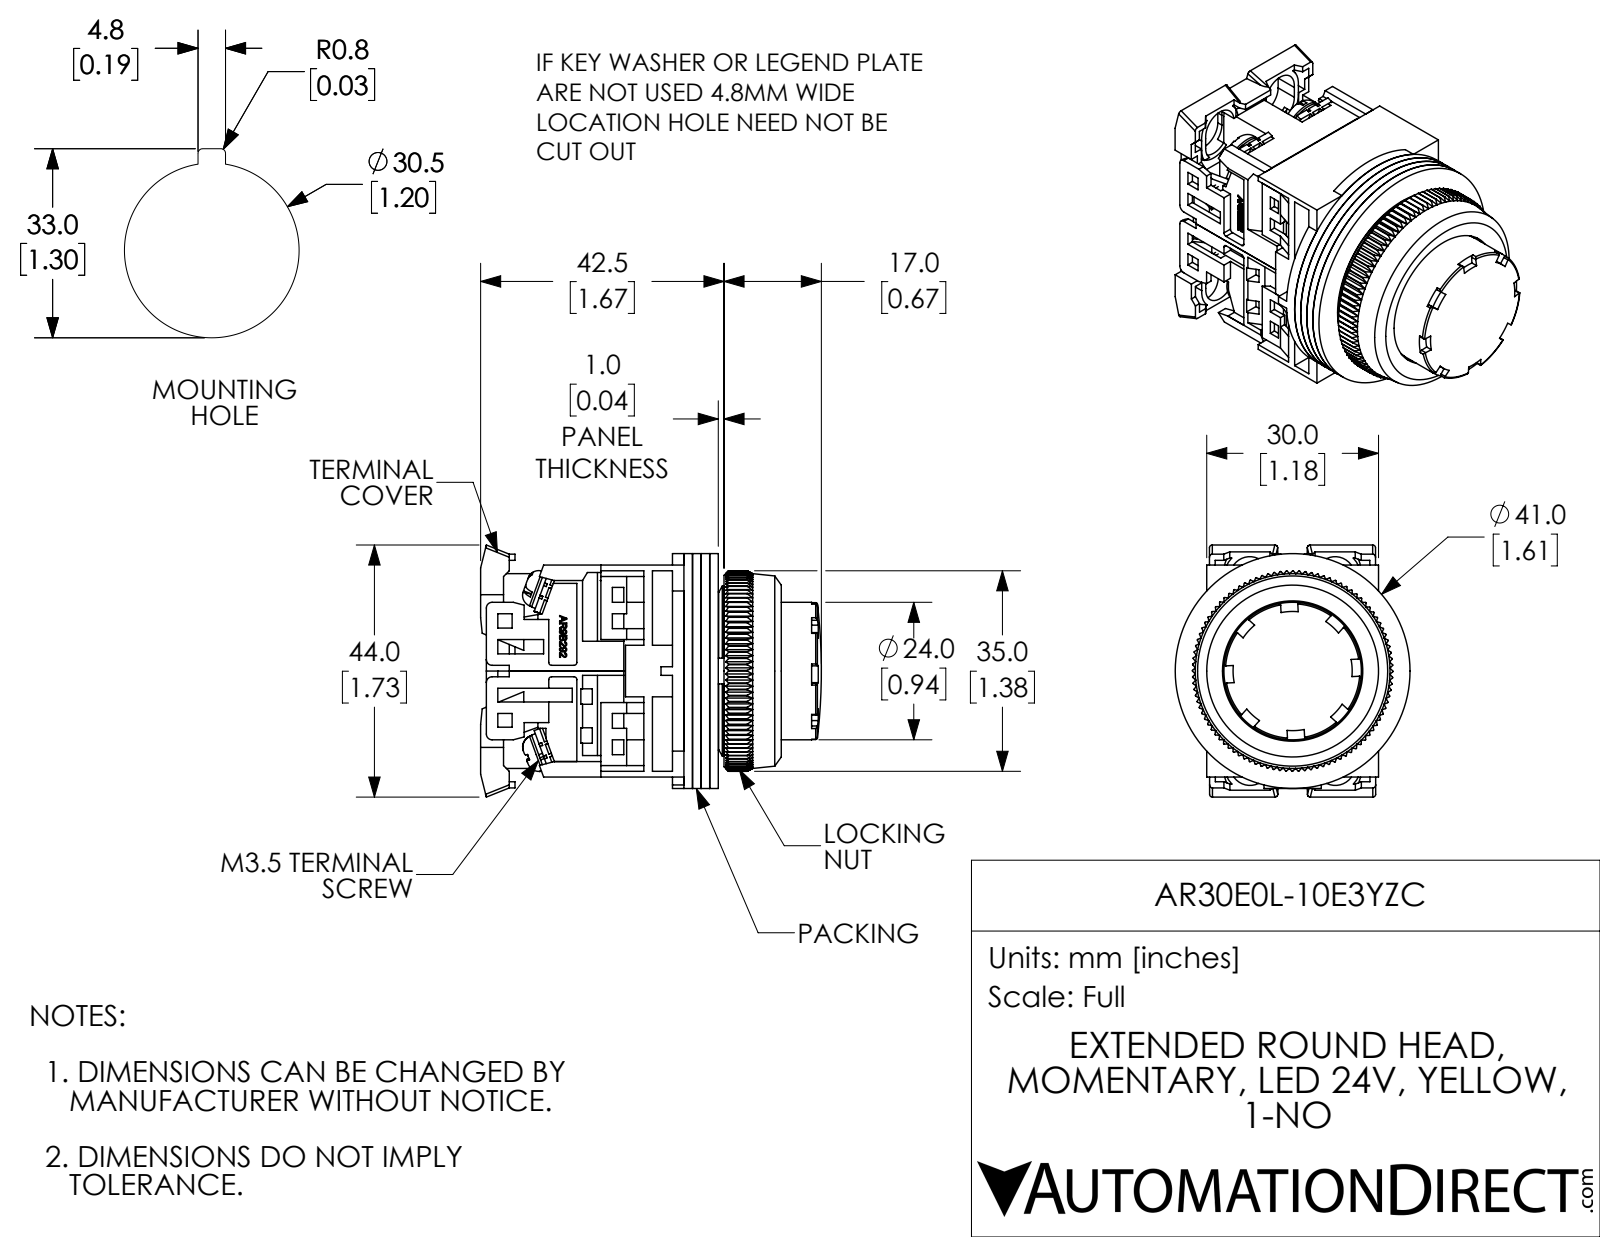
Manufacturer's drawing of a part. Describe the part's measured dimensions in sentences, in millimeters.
The part is named "AR30E0L-10E3YZC". Its 3-D file was written by "SolidWorks 2017 (AUTOMOTIVE_DESIGN)". It is 25 solids with 2022 faces: 1378 planar, 323 cylindrical and 321 other. Overall it measures 59.5 by 44 by 41 millimeters. Its volume is 34 720 cubic millimeters and its surface area 38 610 square millimeters. Round holes: 8 of diameter 3.5, 4 of diameter 3.6, 1 of diameter 3, 1 of diameter 12, 1 of diameter 18, 1 of diameter 18.5, 1 of diameter 20, 1 of diameter 24, 1 of diameter 24.5, 1 of diameter 28.5, 1 of diameter 31.8. Round bosses or shafts: 4 of diameter 6.6, 4 of diameter 3.5, 1 of diameter 41, 1 of diameter 30, 1 of diameter 22, 1 of diameter 19.7, 1 of diameter 14. Partial cylindrical surfaces (rounded edges, fillets, slot ends): 16 of radius 0.3, 16 of radius 1.5, 12 of radius 0.5, 4 of radius 1, 4 of radius 3.5, 4 of radius 4.5, 2 of radius 3, 1 of radius 10.1. The main face-to-face distances are 1.5, 3, 1, 4.5, 20.6, 36, 16.1, 2, 34.5, 17.5. The hole center spacings are 14.7, 15.5.
